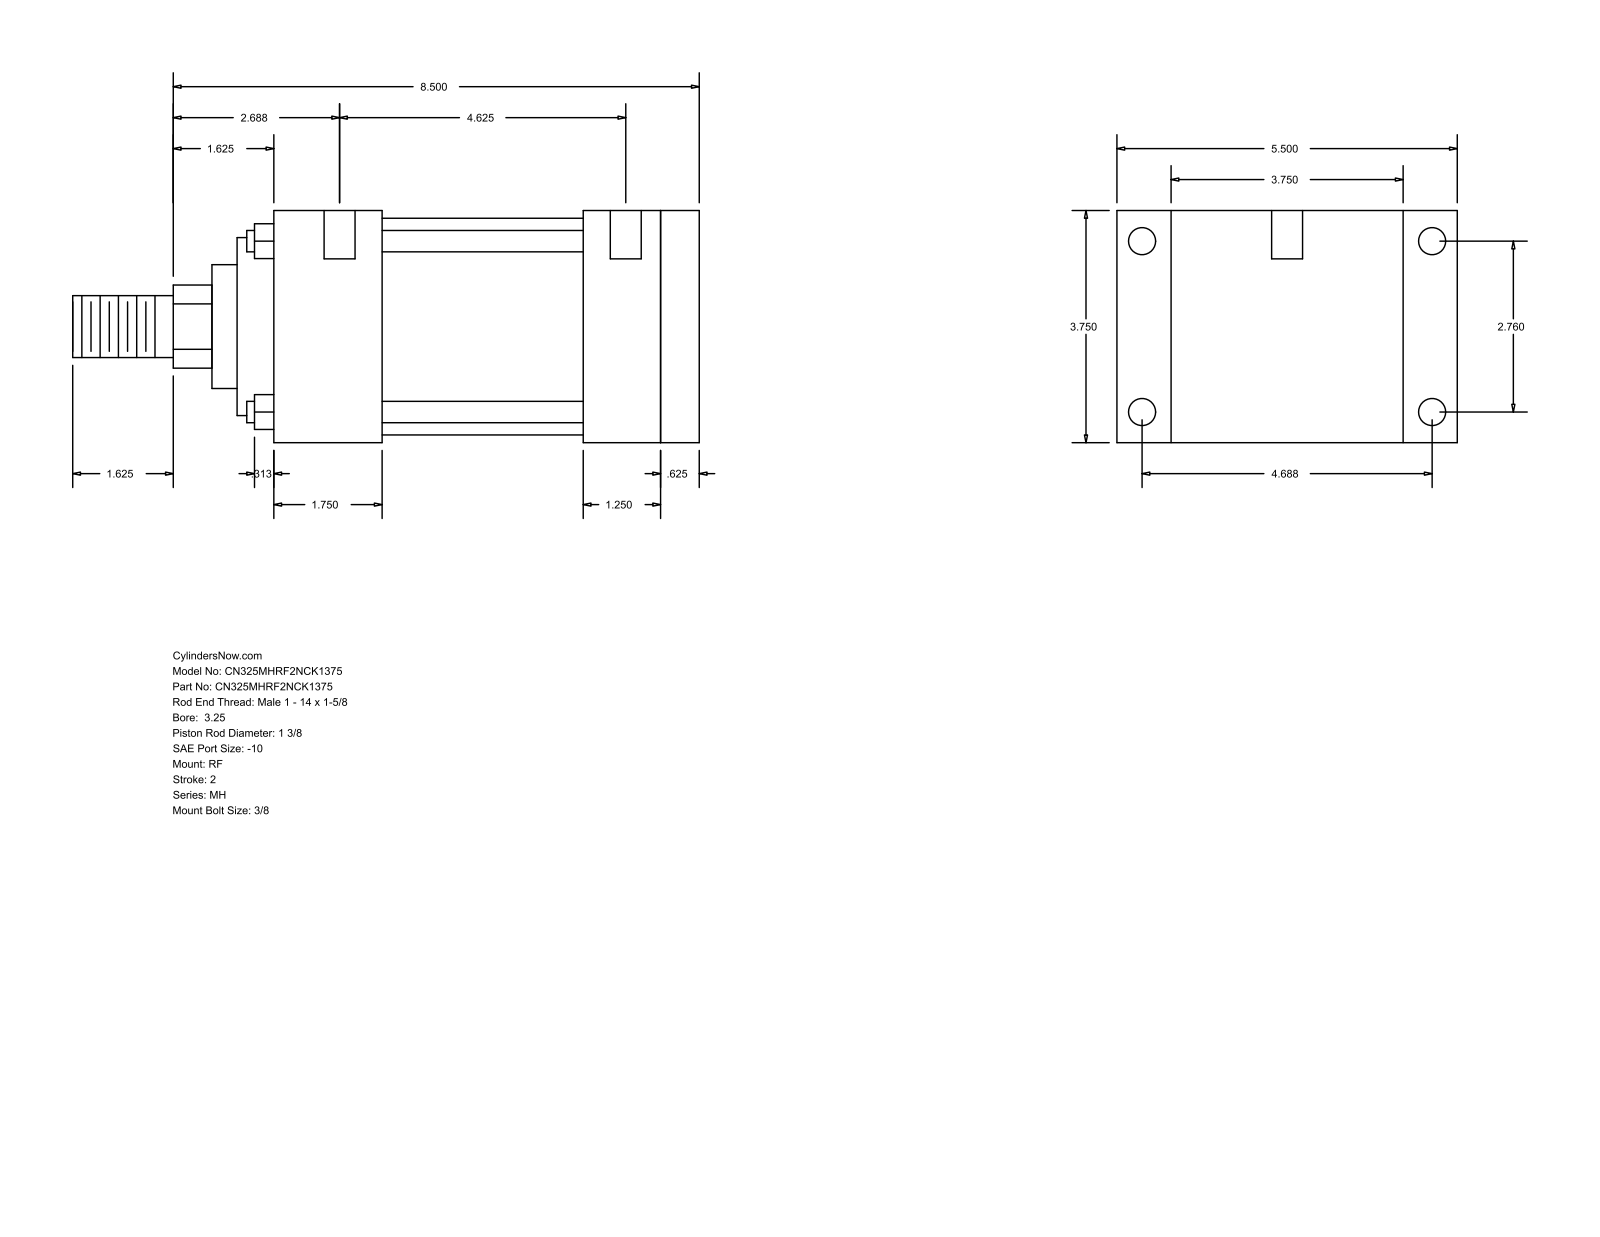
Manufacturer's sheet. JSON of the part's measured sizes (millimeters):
{"part_name": "MH_RF__0325_1.375", "step_written_by": "GSSL Pune (CONFIG_CONTROL_DESIGN)", "units": "millimeters", "bodies": {"solids": 0, "faces": 94, "planar": 65, "cylindrical": 29, "other": 0}, "overall_size": [257.18, 139.7, 95.25], "round_holes": [[5.56, 4], [11.13, 4], [12.7, 2]], "round_bosses_or_shafts": [[8.76, 4], [88.9, 1], [73.03, 1], [50.8, 1], [34.92, 1], [25.4, 1]], "partial_cylinders_radius": [[17.06, 1]], "face_to_face_distances": [95.24, 174.63, 158.76, 15.87, 22.23, 117.47, 44.45, 114.31, 130.18, 127.01], "hole_center_spacings": [70.1, 119.06, 123.83, 138.16, 1.59, 4.76, 117.48, 119.07]}
